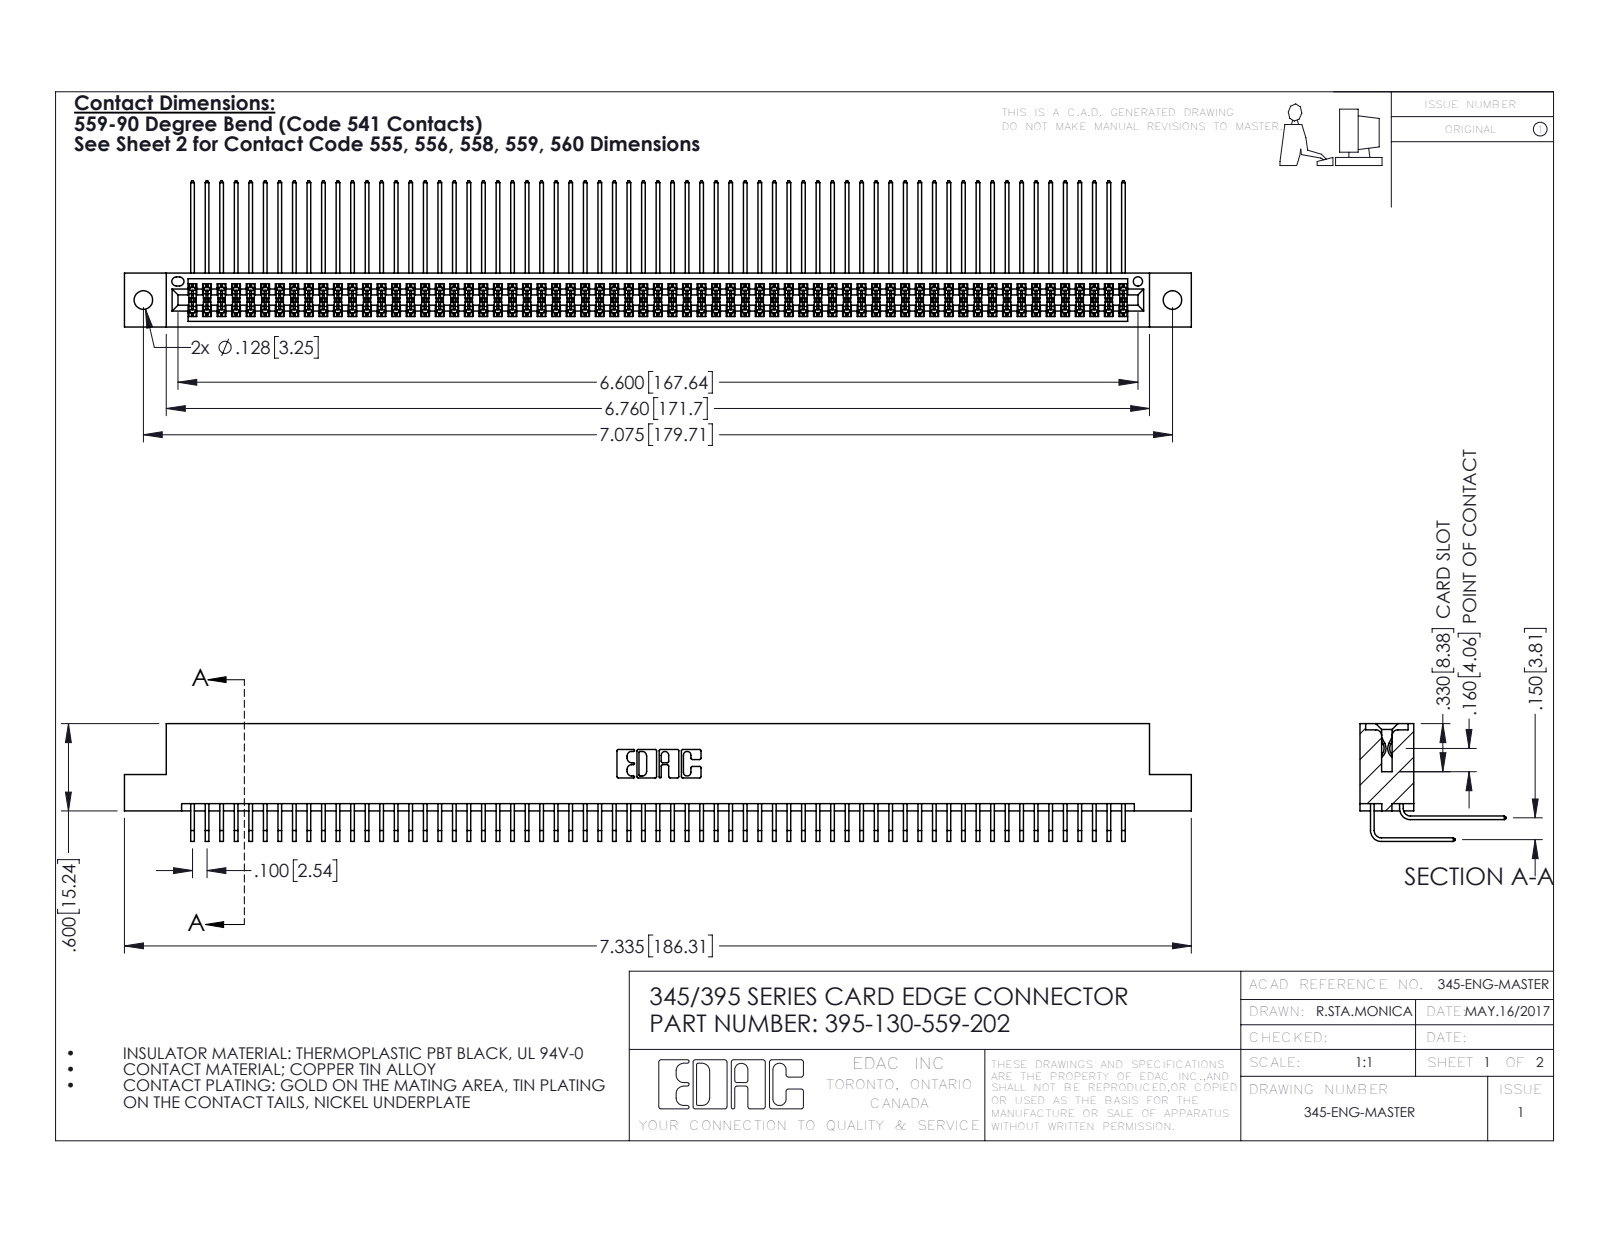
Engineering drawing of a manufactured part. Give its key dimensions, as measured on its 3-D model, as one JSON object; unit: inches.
{"part_name": "345-292-001_559 Tail - 2; 345 Part_Flush Mounting Lugs - 0.128 Dia; 395-130-559-202; 345-292-001_558 559 Tail - 1", "step_written_by": "SolidWorks 2016 (CONFIG_CONTROL_DESIGN)", "units": "inches", "bodies": {"solids": 131, "faces": 6886, "planar": 4630, "cylindrical": 2256, "other": 0}, "overall_size": [7.335, 1.005, 0.809], "volume_in3": 1.161, "surface_area_in2": 49.32, "round_holes": [[0.128, 2], [0.064, 1]], "partial_cylinders_radius": [[0.006, 196], [0.01, 22], [0.007, 6], [0.031, 6], [0.026, 3], [0.014, 2], [0.019, 2], [0.022, 2]], "face_to_face_distances": [0.072, 0.298, 0.2, 0.37, 0.098, 0.272, 0.025, 0.225, 0.175, 0.15], "hole_center_spacings": [0.27, 6.839, 7.075]}
